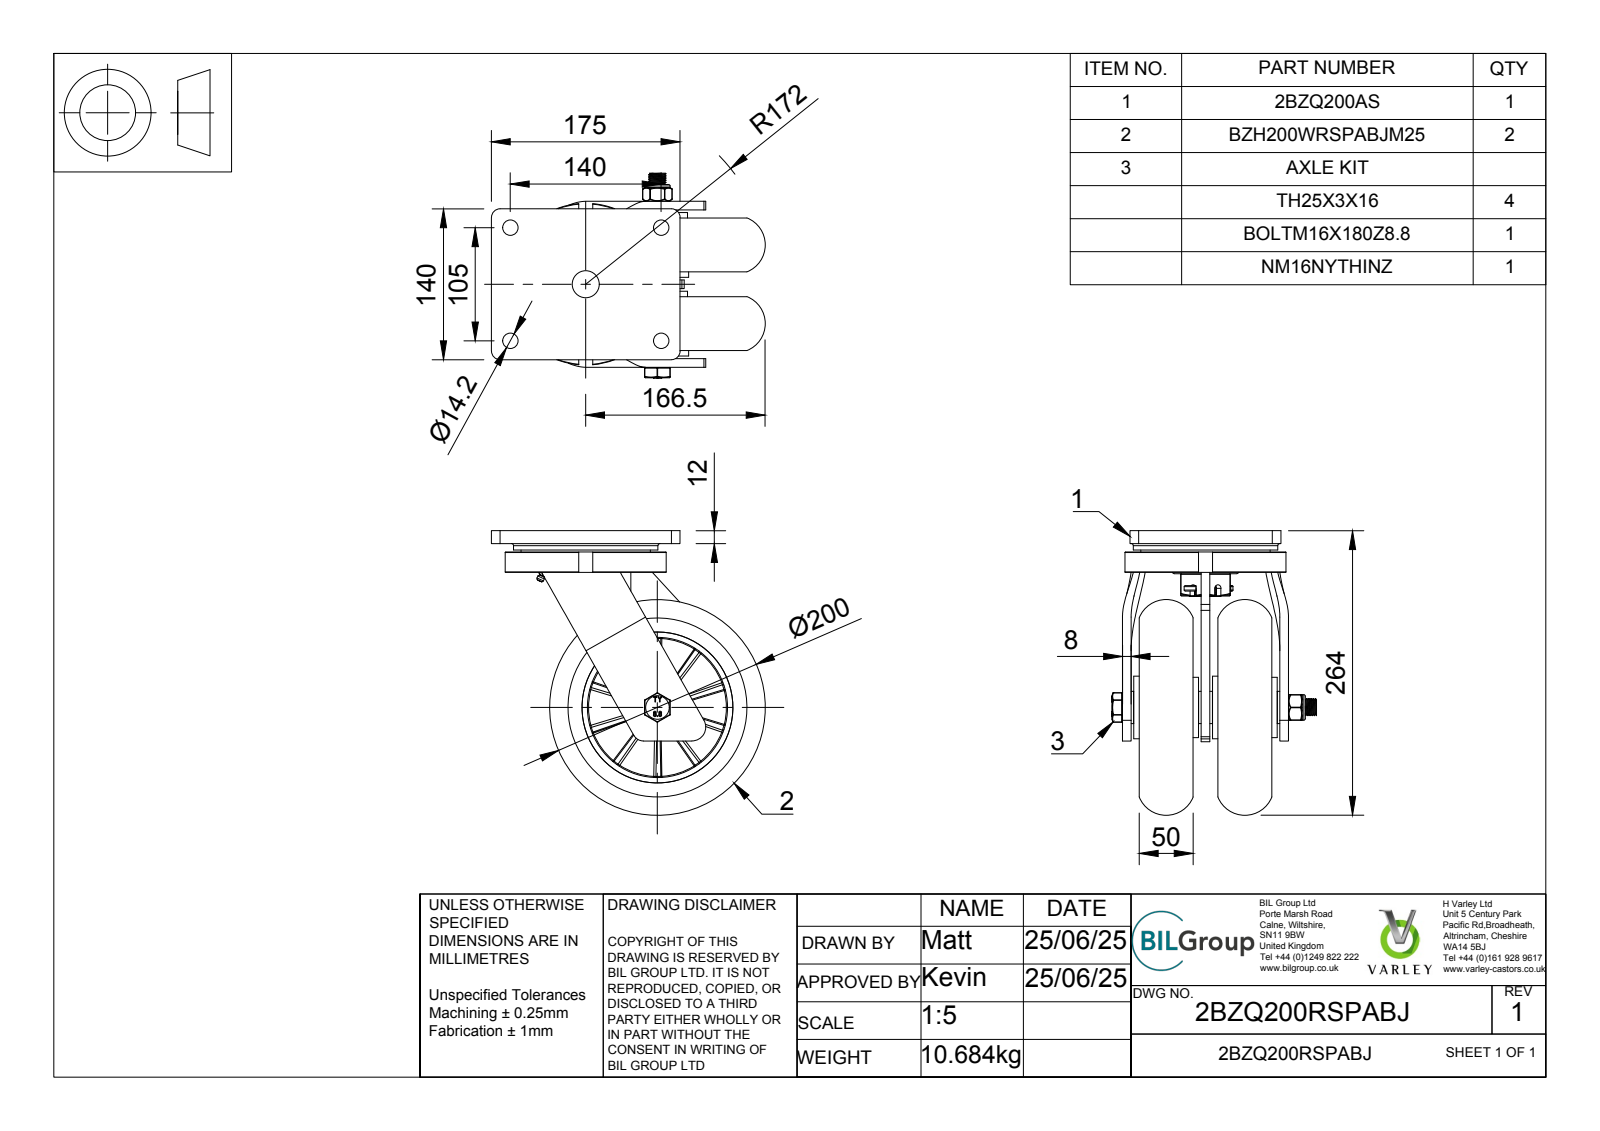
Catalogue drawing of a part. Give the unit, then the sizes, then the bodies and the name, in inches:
Units: inches
Overall size (bounding box): 10.394 × 10 × 7.482
Round holes (diameter × count): ⌀0.559 ×4, ⌀0.984 ×2, ⌀0.236 ×1, ⌀0.63 ×1, ⌀0.638 ×1, ⌀0.64 ×1, ⌀0.709 ×1, ⌀1.024 ×1, ⌀1.181 ×1, ⌀1.26 ×1, ⌀1.299 ×1, ⌀1.496 ×1
Round bosses / shafts (diameter × count): ⌀5.906 ×1, ⌀5.276 ×1, ⌀4.724 ×1, ⌀2.283 ×1, ⌀2.205 ×1, ⌀1.85 ×1, ⌀1.614 ×1, ⌀1.378 ×1
Partial cylindrical surfaces — rounded edges, fillets, slot ends (radius × count): R0.02 ×47, R0.035 ×20, R0.315 ×5, R0.026 ×4, R0.039 ×4, R0.05 ×4, R0.128 ×3, R0.138 ×3
Main face-to-face distances: 2.874, 0.61, 2.264, 0.295, 2.579, 1.614, 0.472, 0.276, 2.303, 0.315
Hole centre spacings: 3.445, 4.134, 5.512, 6.89
Volume: 175.4 in³ · Surface area: 1 032 in²
Bodies: 82 solids, 2769 faces (802 planar, 435 cylindrical, 1532 other)
Part name (STEP PRODUCT): 2BZQ200RSPABJ v4; 2BZQ200AS v1; FABRICATED STEEL TOP PLATE; TOP PLATE (+8 more)
STEP written by: Autodesk Translation Framework v14.10.0.0 (AUTOMOTIVE_DESIGN)
